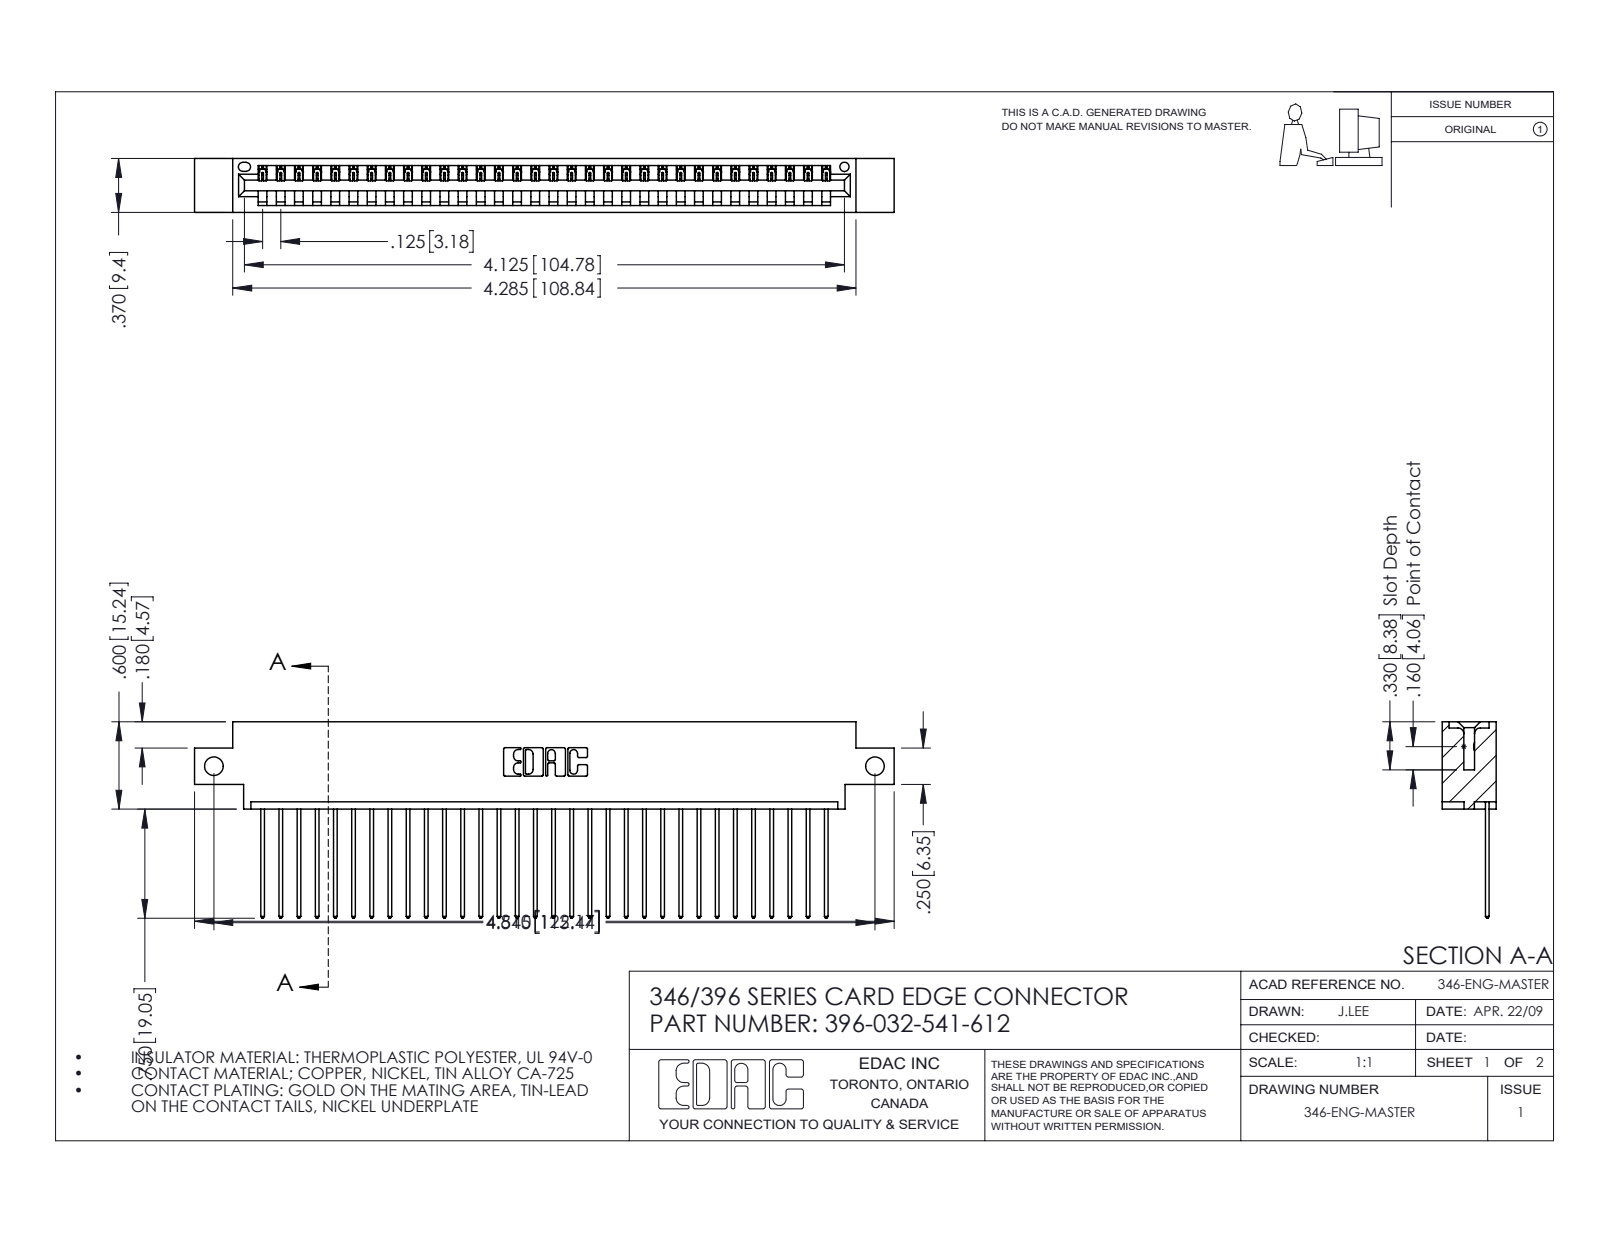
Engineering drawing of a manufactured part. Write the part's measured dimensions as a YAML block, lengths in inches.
part_name: "396-032-541-612; 346 Part_0.170 Offset - Side Mount; 345-292-001_345-293-141"
step_written_by: "SolidWorks 2016 (CONFIG_CONTROL_DESIGN)"
units: inches
bodies: {solids: 33, faces: 1982, planar: 1360, cylindrical: 622, other: 0}
overall_size: [4.81, 1.35, 0.37]
volume: 0.701
surface_area: 23.09
round_holes:
  - {diameter: 0.128, count: 2}
  - {diameter: 0.064, count: 1}
partial_cylinders:
  - {radius: 0.006, count: 64}
  - {radius: 0.01, count: 64}
  - {radius: 0.01, count: 22}
  - {radius: 0.007, count: 6}
  - {radius: 0.031, count: 6}
  - {radius: 0.026, count: 3}
  - {radius: 0.031, count: 2}
  - {radius: 0.04, count: 2}
face_to_face_distances: [0.048, 0.322, 0.37, 0.25, 0.072, 0.298, 0.025, 0.148, 0.222, 0.1]
hole_center_spacings: [4.545]
